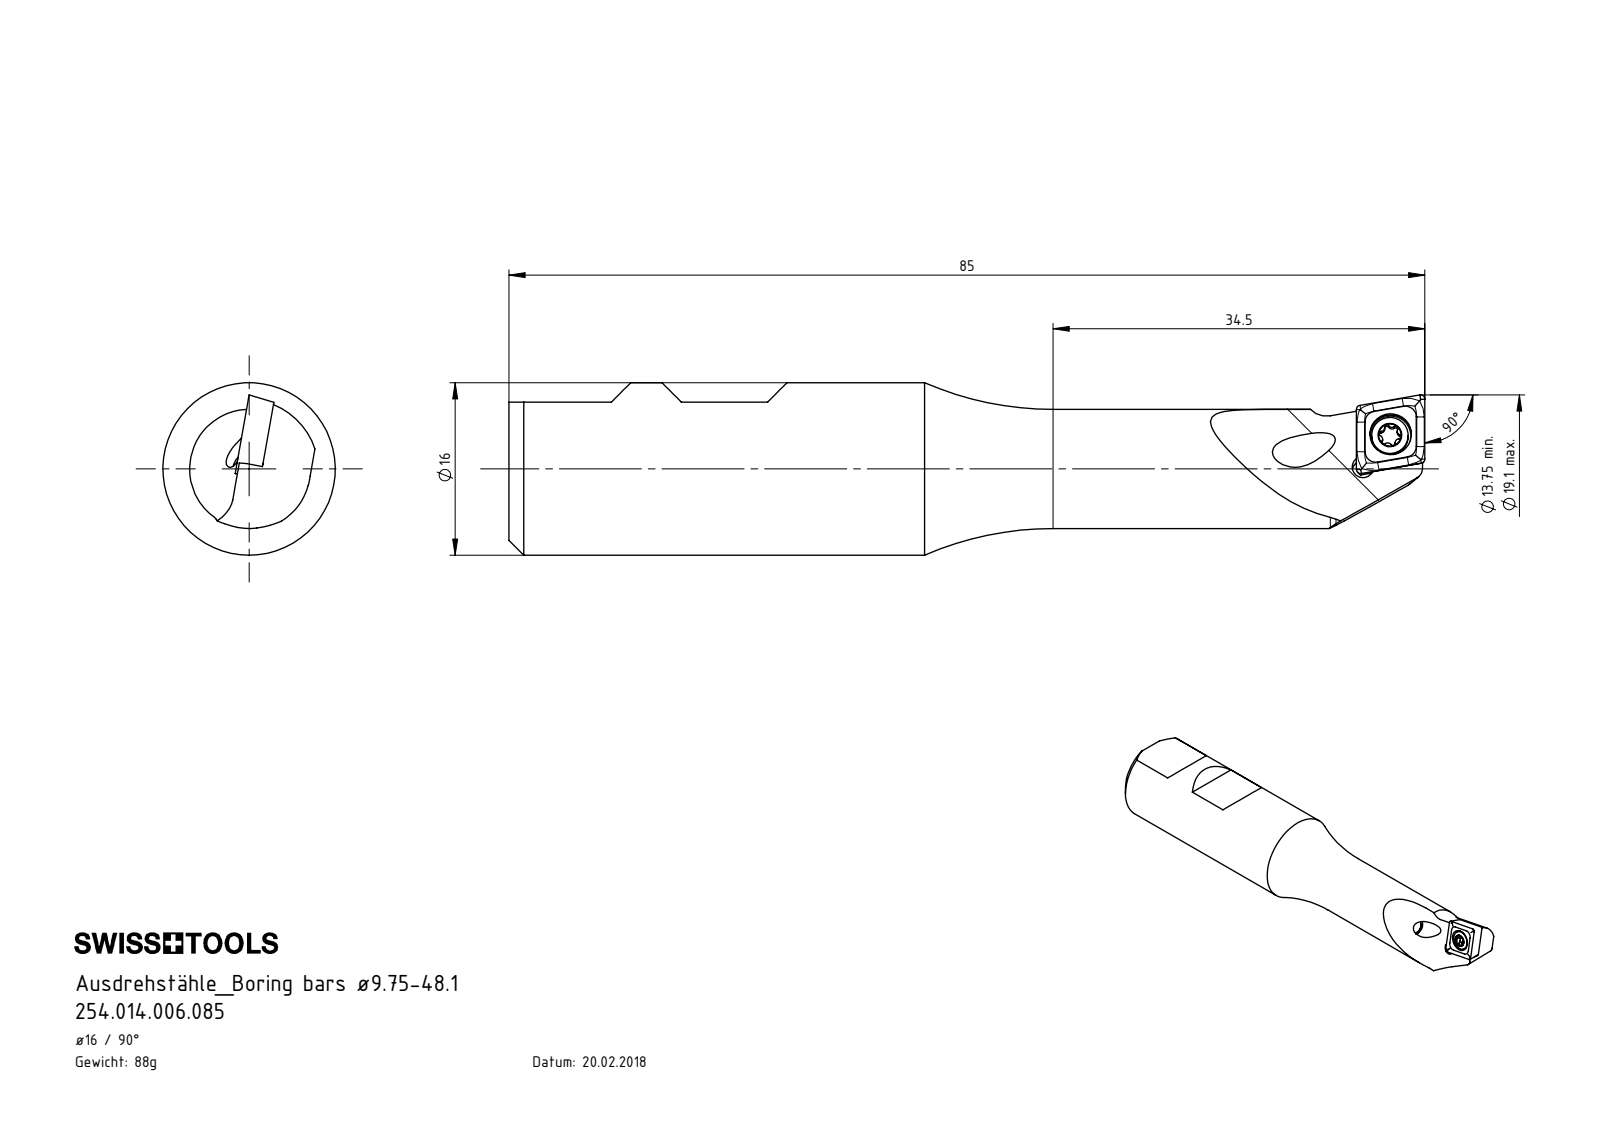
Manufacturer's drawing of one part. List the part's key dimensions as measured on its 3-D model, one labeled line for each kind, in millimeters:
Part name (STEP PRODUCT): 254.014.006.085; WCA-ER2.001.006_A; CCMT060204; B14-WCA.K11.085_A
STEP written by: SolidWorks 2017 (CONFIG_CONTROL_DESIGN)
Units: millimetres
Bodies: 3 solids, 130 faces (33 planar, 41 cylindrical, 56 other)
Overall size (bounding box): 85 × 16 × 16
Volume: 11 149 mm³ · Surface area: 4 644 mm²
Round holes (diameter × count): ⌀3 ×2, ⌀2 ×1, ⌀2.05 ×1, ⌀2.8 ×1, ⌀3.85 ×1
Round bosses / shafts (diameter × count): ⌀16 ×1, ⌀11.05 ×1, ⌀3.4 ×1, ⌀2.5 ×1
Partial cylindrical surfaces — rounded edges, fillets, slot ends (radius × count): R0.21 ×6, R0.36 ×5, R0.36 ×1, R1 ×1, R5.7 ×1, R6.5 ×1, R8 ×1
Main face-to-face distances: 2.17, 2.18, 10.25, 4.51, 4.52, 6.69, 6.9, 2.39, 2.38, 78.76
Hole centre spacings: 3.89, 4
